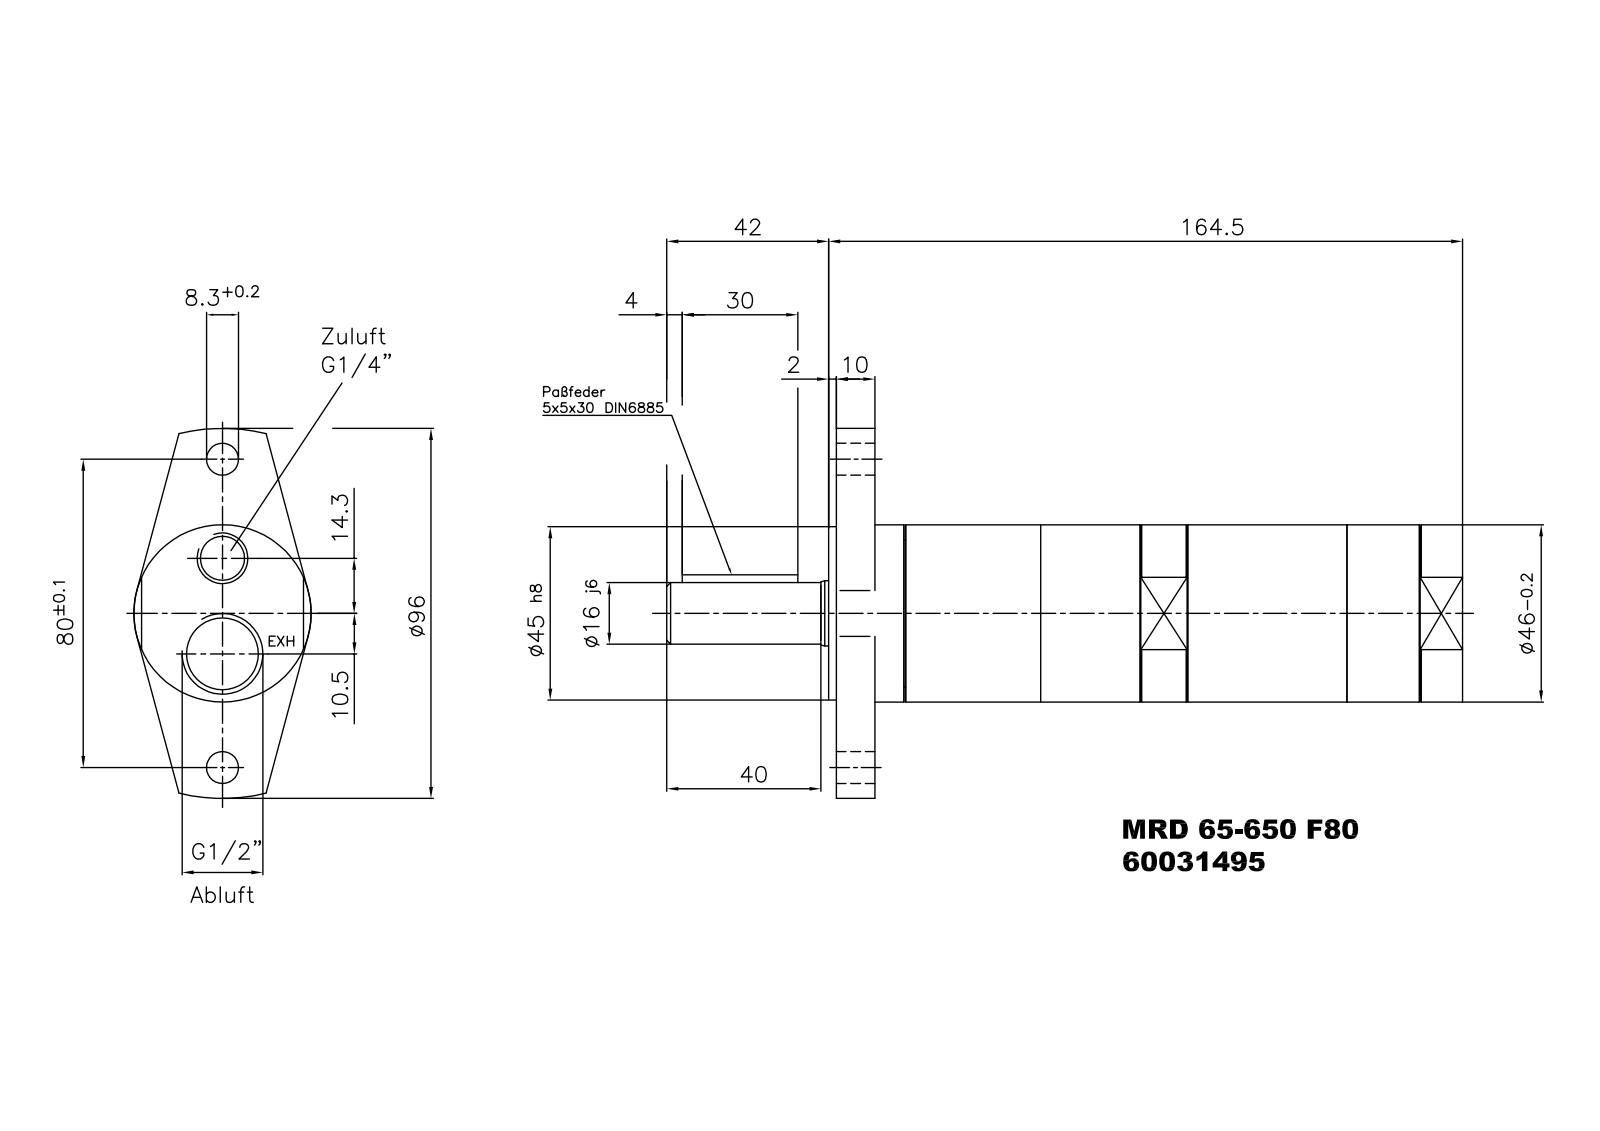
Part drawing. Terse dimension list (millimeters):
name: MRD 65-650 500 290 F80 206,5mm
written by: Autodesk Inventor 2013 (AUTOMOTIVE_DESIGN)
unit: mm
bodies: 1 solid, 155 faces (98 planar, 23 cylindrical, 34 other)
size: 206.5 × 96 × 46
volume: 290 366 mm³; area: 37 212 mm²
holes: 2× ⌀8.3, 1× ⌀1.6, 1× ⌀11.45, 1× ⌀17.5, 1× ⌀18.63
bosses: 1× ⌀46, 1× ⌀45, 1× ⌀40, 1× ⌀16.95, 1× ⌀16
rounds: 2× R2.5, 1× R48
face distances: 10, 12, 2, 152.5, 164.5, 162.5, 132.5, 30, 134.5, 55
hole spacings: 40, 10.5, 14.3, 24.8, 25.7, 29.5, 50.5, 54.3
